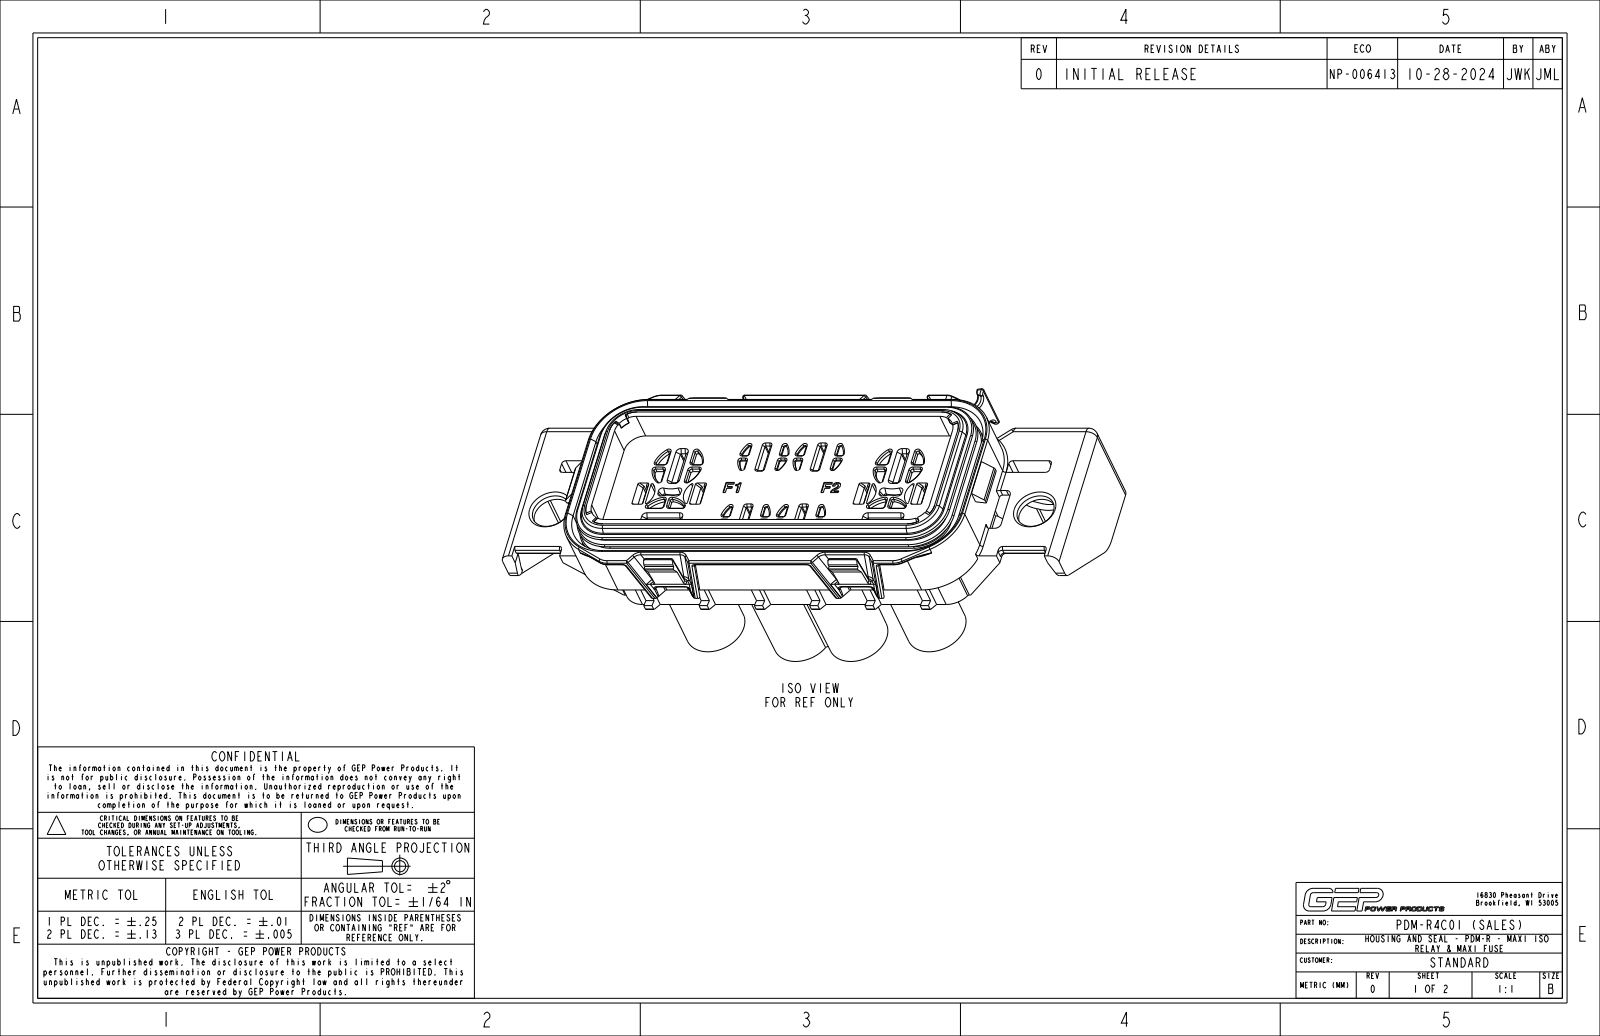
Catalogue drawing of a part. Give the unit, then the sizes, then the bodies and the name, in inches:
Units: inches
Overall size (bounding box): 6.417 × 2.392 × 2.37
Round holes (diameter × count): ⌀0.541 ×8, ⌀0.386 ×4, ⌀0.413 ×4, ⌀0.492 ×2
Round bosses / shafts (diameter × count): ⌀0.659 ×2, ⌀0.197 ×1, ⌀0.098 ×1
Partial cylindrical surfaces — rounded edges, fillets, slot ends (radius × count): R0.02 ×209, R0.016 ×134, R0.012 ×70, R0.008 ×48, R0.035 ×39, R0.039 ×26, R0.014 ×16, R0.024 ×16
Main face-to-face distances: 0.079, 1.516, 0.374, 0.098, 0.453, 0.217, 0.071, 0.295, 0.276, 0.138
Hole centre spacings: 0.491, 0.521, 2.511, 2.551, 3.141, 0.638, 0.68, 0.705
Volume: 8.161 in³ · Surface area: 168.2 in²
Bodies: 5 solids, 3262 faces (1506 planar, 867 cylindrical, 889 other)
Part name (STEP PRODUCT): C26-1012-2C_SALES_NCF; C14-1013_INSTALLED_NCF; PDM-RS_INSTALLED_NCF_ASM; PDM-R4C01_NCF_ASM
STEP written by: CREO PARAMETRIC BY PTC INC, 2024014 (CONFIG_CONTROL_DESIGN)
